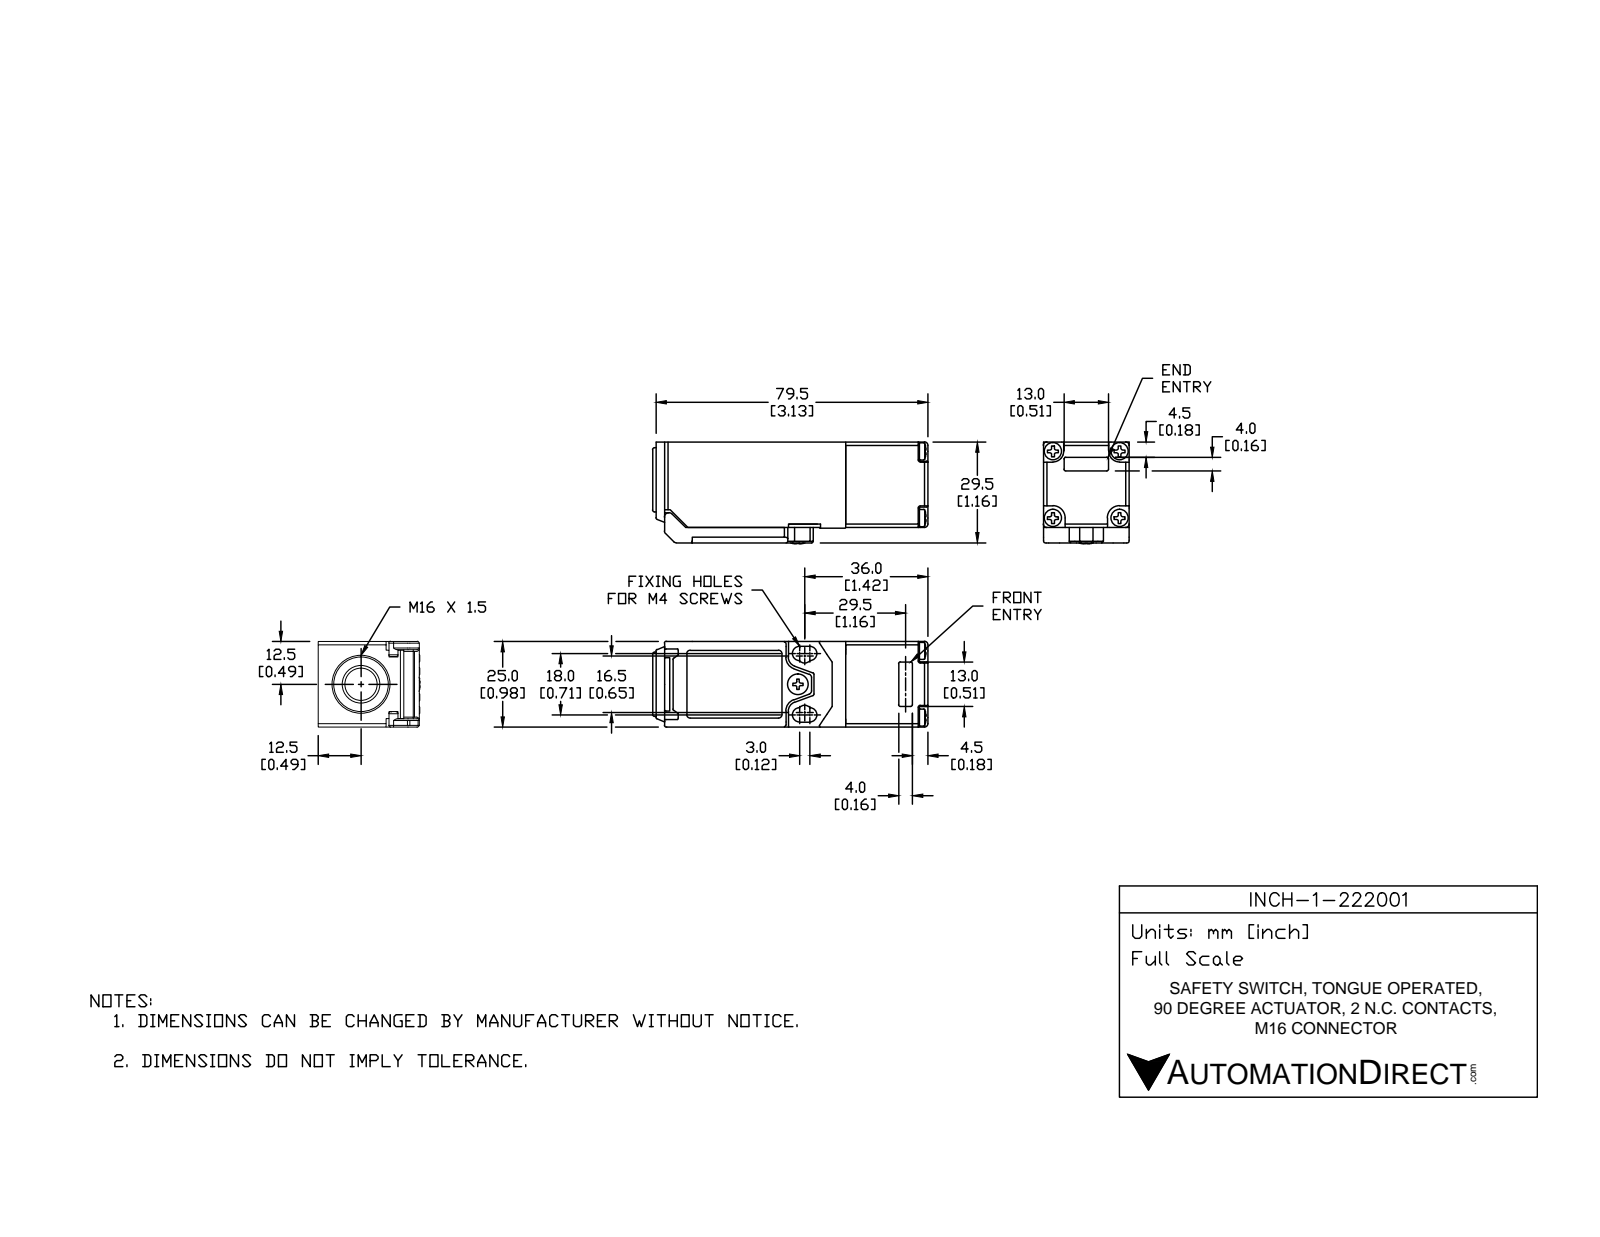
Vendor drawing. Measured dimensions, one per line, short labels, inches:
name: INCH-1-222001
written by: SolidWorks 2014 (AUTOMOTIVE_DESIGN)
unit: in
bodies: 14 solids, 1863 faces (738 planar, 677 cylindrical, 448 other)
size: 3.169 × 1.172 × 0.984
volume: 1.453 in³; area: 40.72 in²
holes: 5× ⌀0.126, 4× ⌀0.094, 2× ⌀0.059, 2× ⌀0.063, 2× ⌀0.071, 2× ⌀0.087, 2× ⌀0.142, 1× ⌀0.055, 1× ⌀0.098, 1× ⌀0.102, 1× ⌀0.197, 1× ⌀0.217
bosses: 5× ⌀0.102, 4× ⌀0.197, 4× ⌀0.079, 2× ⌀0.138, 1× ⌀0.74, 1× ⌀0.531, 1× ⌀0.213, 1× ⌀0.118
rounds: 236× R0.02, 85× R0.012, 24× R0.004, 24× R0.039, 10× R0.031, 6× R0.083, 6× R0.11, 4× R0.008
face distances: 0.984, 0.079, 0.039, 0.906, 0.02, 0.874, 0.024, 0.945, 0.929, 0.913
hole spacings: 0.543, 0.768, 0.171, 0.187, 0.423, 0.426, 0.45, 0.581
